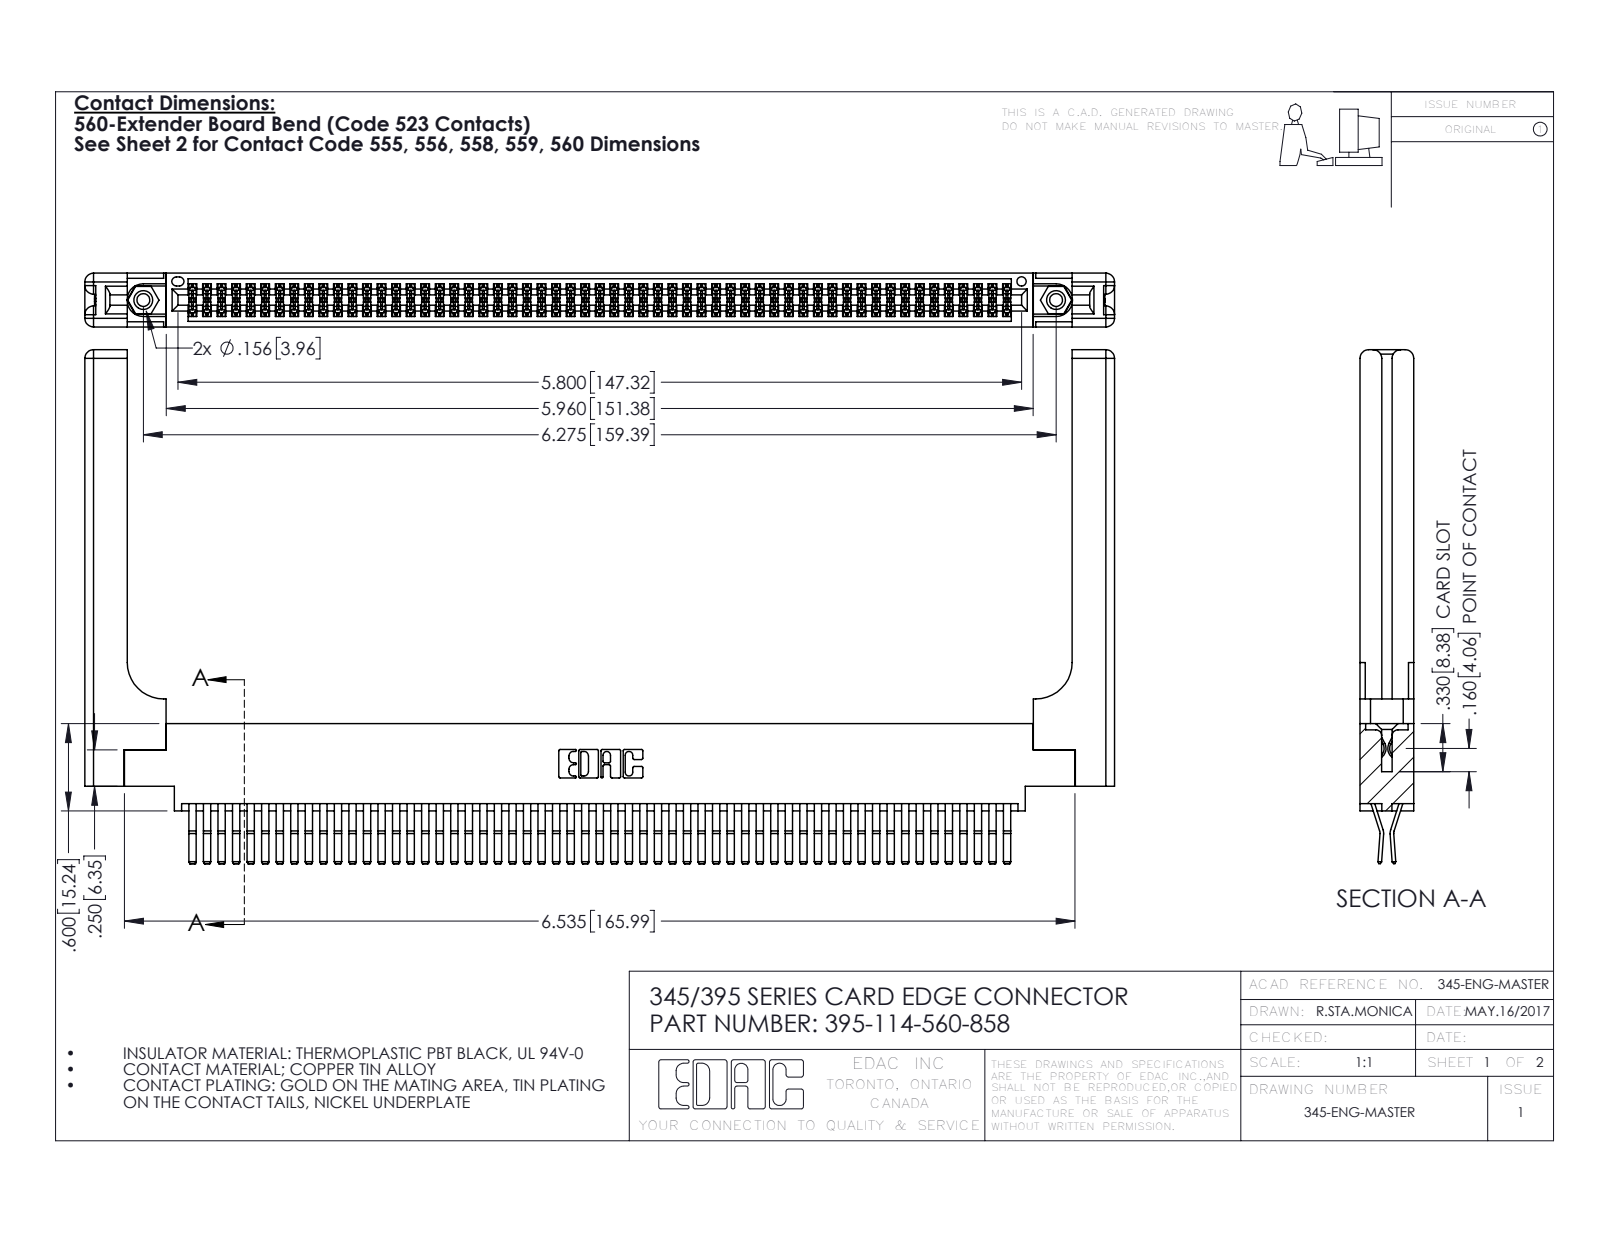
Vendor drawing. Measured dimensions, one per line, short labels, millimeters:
name: 395-114-560-858; 345-292-001_560 Tail; 345-220-058_345-220-058; 345 Part_0.170 Offset - 0.156 Dia-TH (+1 more)
written by: SolidWorks 2016 (CONFIG_CONTROL_DESIGN)
unit: mm
bodies: 119 solids, 6314 faces (3994 planar, 2260 cylindrical, 60 other)
size: 179.8 × 89.7 × 9.4
volume: 26 710 mm³; area: 34 370 mm²
holes: 2× ⌀2.3, 2× ⌀3.2, 2× ⌀4, 1× ⌀1.6
bosses: 2× ⌀3.9
rounds: 172× R0.2, 22× R0.3, 16× R1.5, 6× R0.2, 6× R0.8, 3× R0.7, 2× R0.3, 2× R0.4
face distances: 1.8, 9.4, 7.6, 0.6, 2.5, 6.9, 5.1, 5.7, 4.4, 3.8
hole spacings: 6.9, 153.4, 159.4
